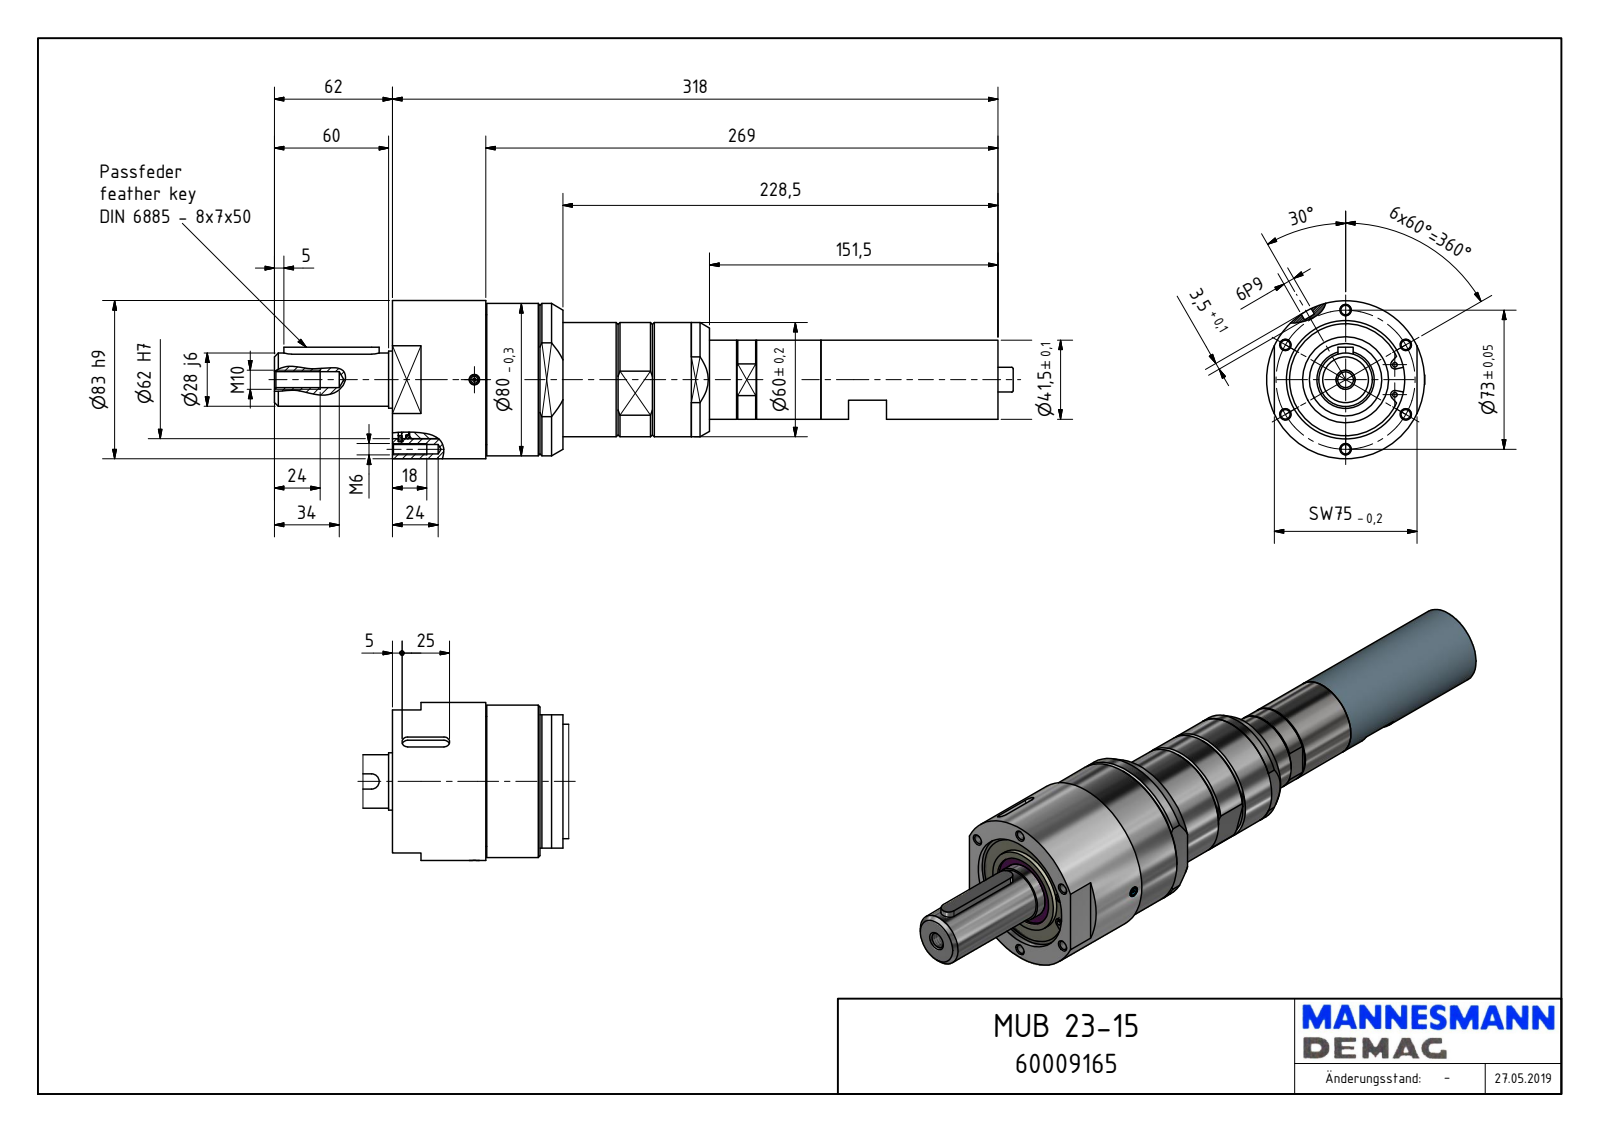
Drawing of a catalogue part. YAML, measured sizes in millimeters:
part_name: "MUB 23-15_60009165"
step_written_by: "Autodesk Inventor 2018 (AUTOMOTIVE_DESIGN)"
units: millimeters
bodies: {solids: 1, faces: 576, planar: 162, cylindrical: 255, other: 159}
overall_size: [388, 83, 83]
volume: 893090
surface_area: 97894
round_holes:
  - {diameter: 4.92, count: 6}
  - {diameter: 4, count: 4}
  - {diameter: 1.55, count: 3}
  - {diameter: 2, count: 2}
  - {diameter: 2.5, count: 2}
  - {diameter: 5, count: 2}
  - {diameter: 5.5, count: 2}
  - {diameter: 8.57, count: 2}
  - {diameter: 8.38, count: 1}
  - {diameter: 8.5, count: 1}
  - {diameter: 13, count: 1}
  - {diameter: 36.5, count: 1}
round_bosses_or_shafts:
  - {diameter: 5, count: 2}
  - {diameter: 3.6, count: 2}
  - {diameter: 3.3, count: 2}
  - {diameter: 83, count: 1}
  - {diameter: 80, count: 1}
  - {diameter: 68.18, count: 1}
  - {diameter: 67, count: 1}
  - {diameter: 60, count: 1}
partial_cylinders:
  - {radius: 3.5, count: 94}
  - {radius: 1.6, count: 2}
  - {radius: 2.25, count: 2}
  - {radius: 3, count: 2}
  - {radius: 4, count: 2}
  - {radius: 4.5, count: 1}
  - {radius: 8, count: 1}
  - {radius: 8.1, count: 1}
face_to_face_distances: [49, 0.5, 228.5, 2.5, 151.5, 40.5, 89.5, 318, 269, 49.5]
hole_center_spacings: [36.5, 63.22, 73, 11.89, 12.94, 24.23, 26.77, 26.98]
